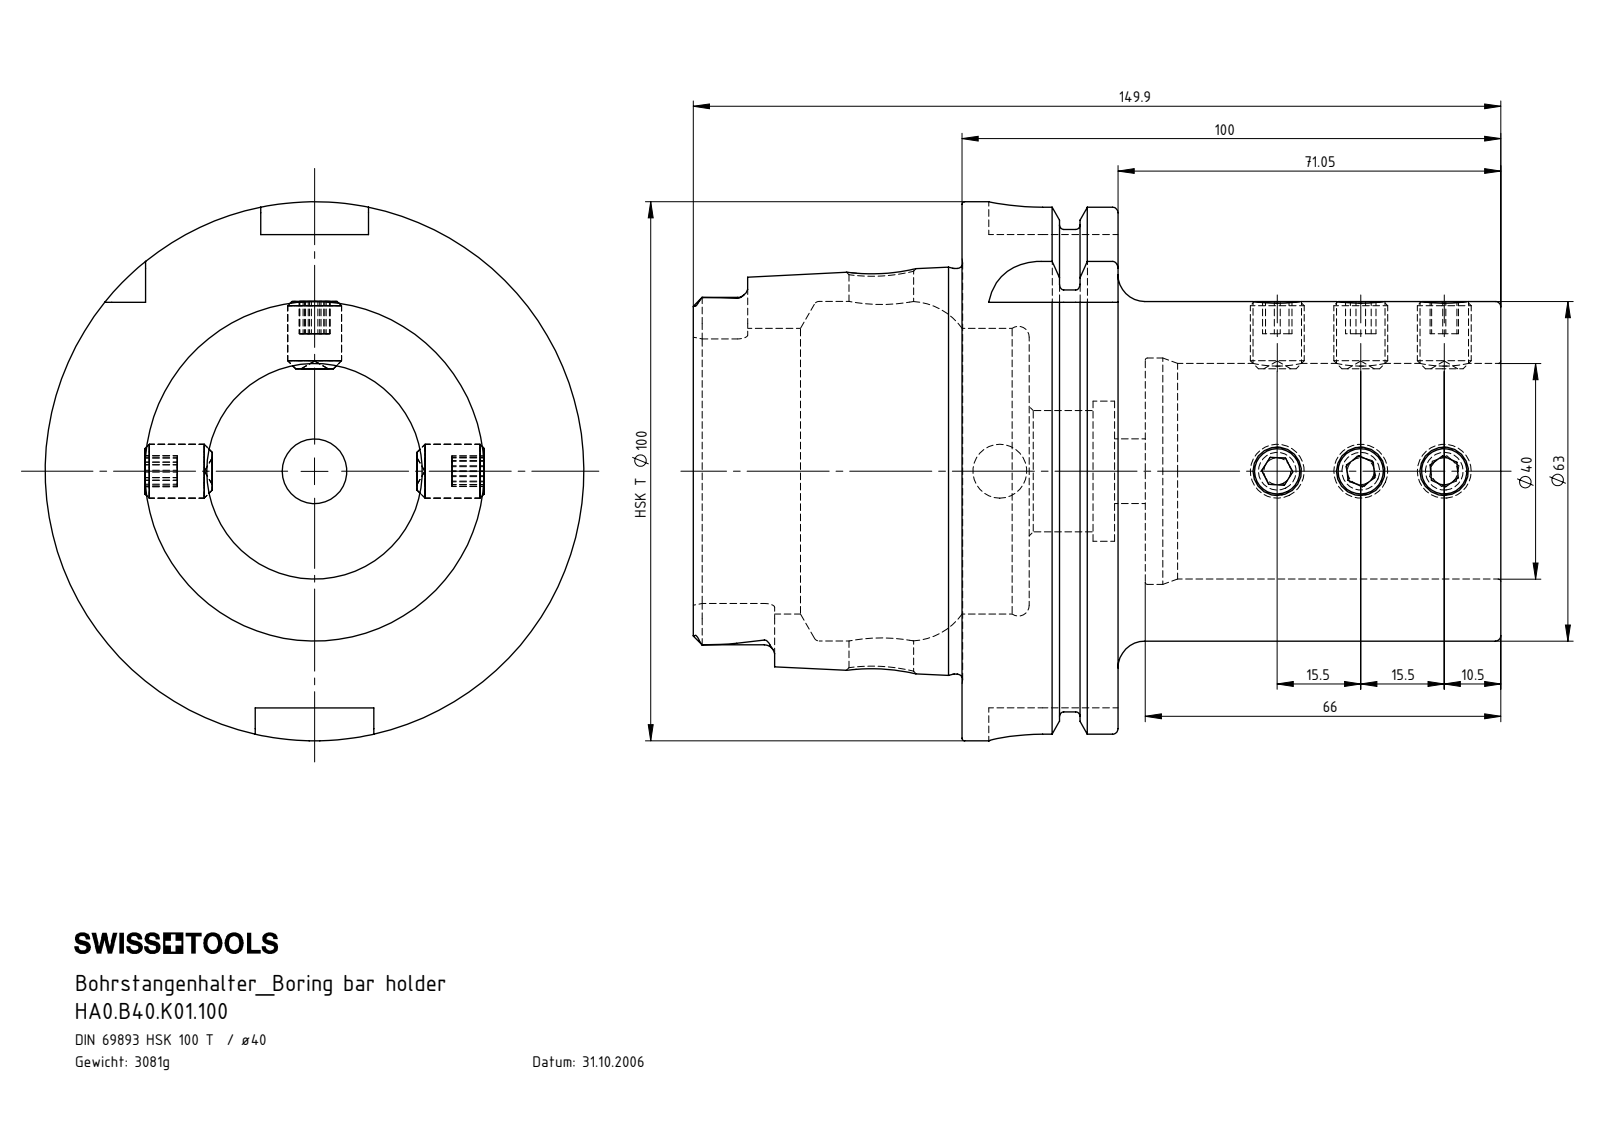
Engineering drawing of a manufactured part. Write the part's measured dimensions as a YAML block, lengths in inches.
part_name: "W10-ER1.001.012; HA0-B40.K01.100_B_Fertigbearbeitung; HA0-B40.K01.100"
step_written_by: "SolidWorks 2012 (AUTOMOTIVE_DESIGN)"
units: inches
bodies: {solids: 10, faces: 331, planar: 122, cylindrical: 86, other: 123}
overall_size: [5.902, 3.937, 3.937]
volume: 23.95
surface_area: 122.3
round_holes:
  - {diameter: 0.354, count: 6}
  - {diameter: 0.472, count: 2}
  - {diameter: 0.394, count: 1}
  - {diameter: 0.886, count: 1}
  - {diameter: 1.024, count: 1}
  - {diameter: 1.575, count: 1}
  - {diameter: 1.654, count: 1}
  - {diameter: 2.087, count: 1}
  - {diameter: 2.48, count: 1}
round_bosses_or_shafts:
  - {diameter: 0.394, count: 6}
  - {diameter: 3.937, count: 1}
  - {diameter: 3.62, count: 1}
  - {diameter: 2.963, count: 1}
partial_cylinders:
  - {radius: 0.075, count: 6}
  - {radius: 0.192, count: 4}
  - {radius: 0.394, count: 4}
face_to_face_distances: [1.14, 3.937, 2.797, 0.49, 0.65, 3.447, 0.848, 1.339, 0.199, 2.598]
hole_center_spacings: [0.61, 1.22, 2.028, 2.638, 2.894, 3.248, 3.504, 4.114]
